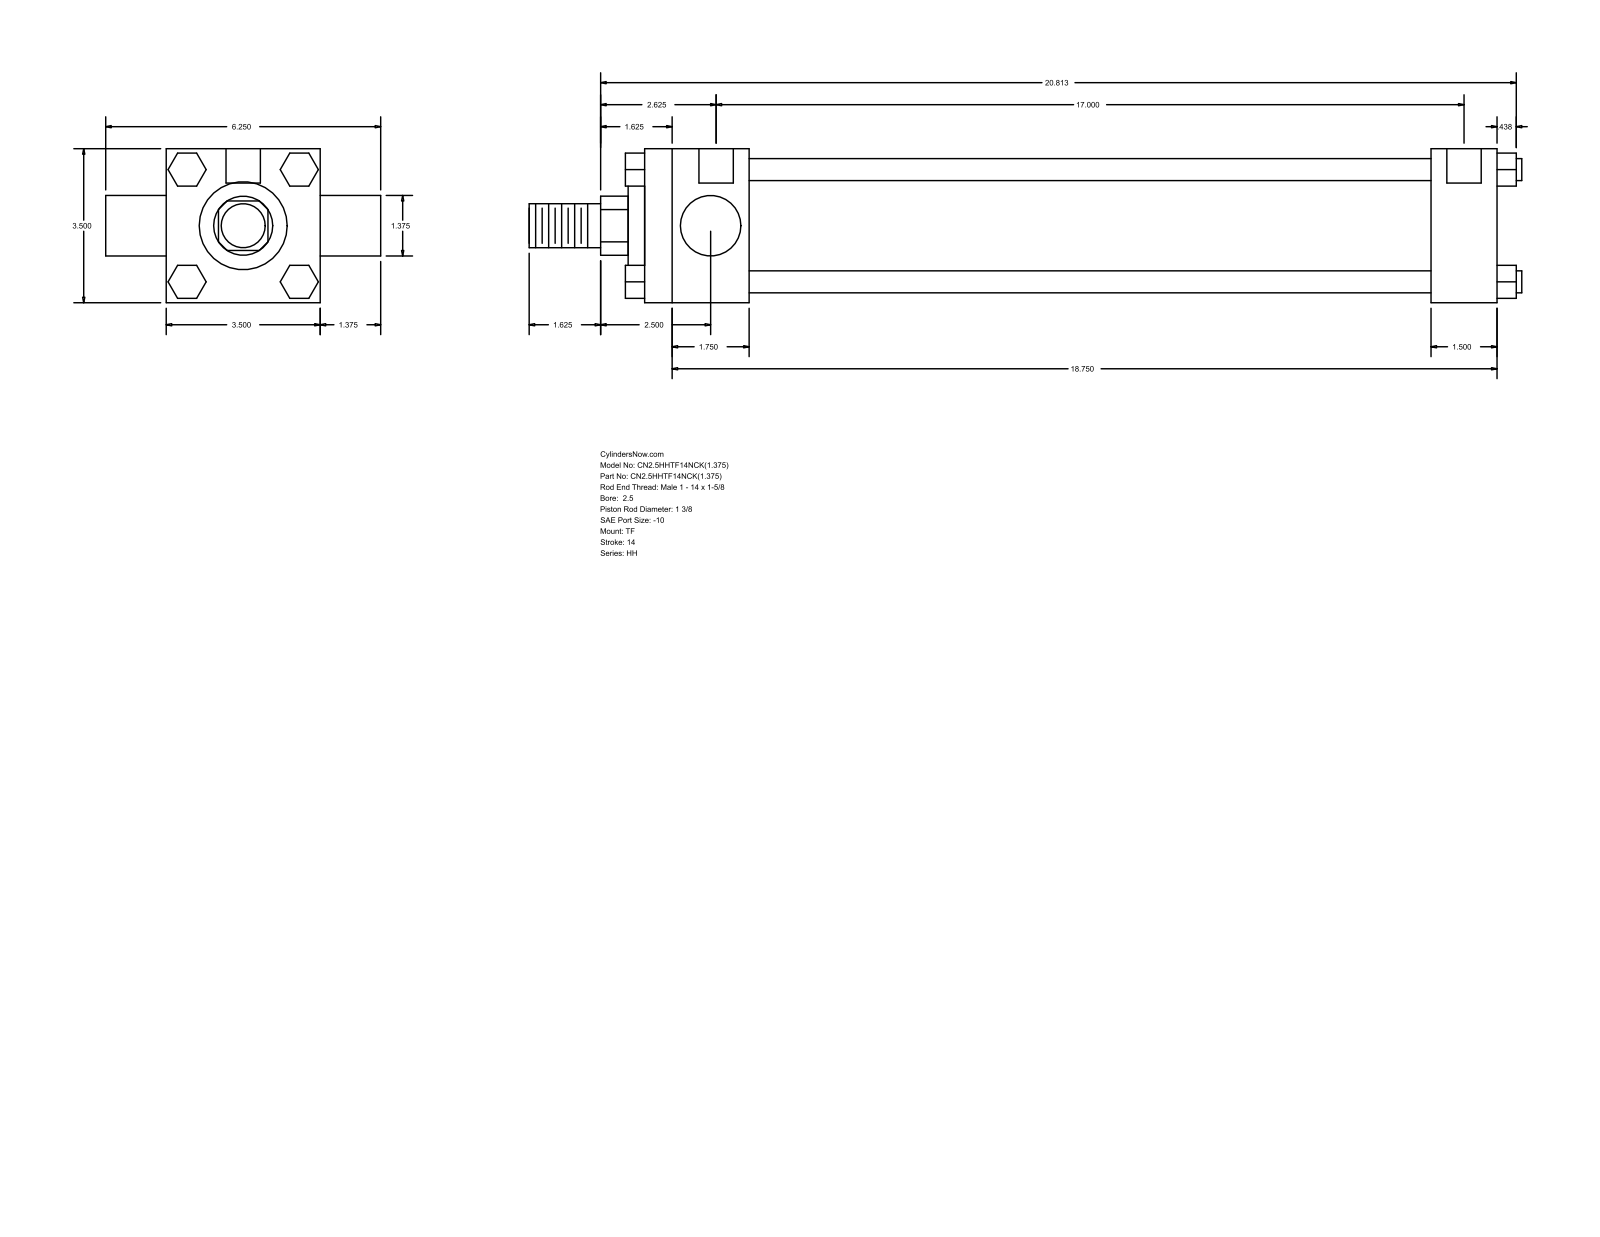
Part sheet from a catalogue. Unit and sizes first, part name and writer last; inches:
Units: inches
Overall size (bounding box): 22.563 × 6.25 × 3.5
Round holes (diameter × count): ⌀0.219 ×3, ⌀0.781 ×2
Round bosses / shafts (diameter × count): ⌀0.5 ×4, ⌀1.375 ×2, ⌀2.875 ×1, ⌀2 ×1, ⌀1 ×1
Partial cylindrical surfaces — rounded edges, fillets, slot ends (radius × count): R0.672 ×1
Main face-to-face distances: 3.5, 19.375, 2.375, 17, 17.875, 15.5, 1.5, 0.75, 1.275, 2.208
Hole centre spacings: 0.062, 17.063, 17, 17.125
Bodies: 0 solids, 120 faces (92 planar, 28 cylindrical, 0 other)
Part name (STEP PRODUCT): HH_TF__0250_1.375
STEP written by: GSSL Pune (CONFIG_CONTROL_DESIGN)
